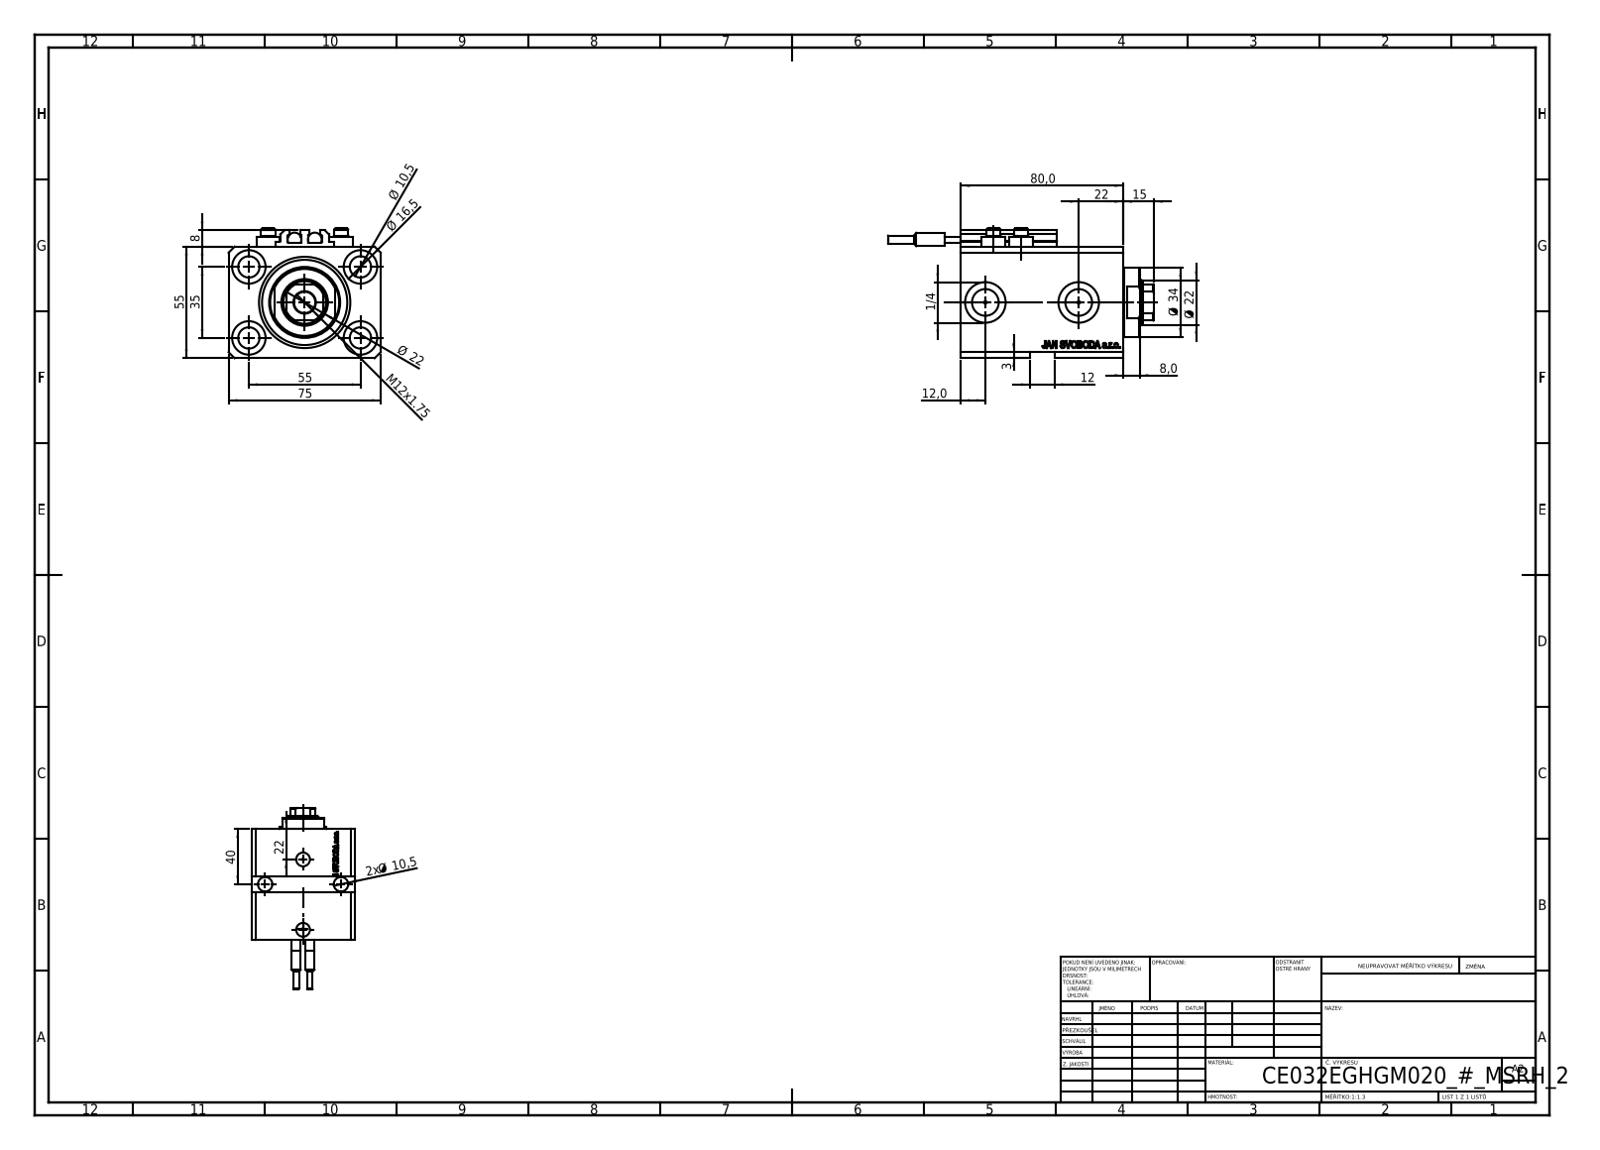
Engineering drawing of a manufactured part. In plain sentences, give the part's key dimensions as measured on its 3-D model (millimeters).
The part is named "V250CE_C_VCP; SWITCH_V250CE; V250CE_E_Body; V250CE_VC_E (+1 more)". Its 3-D file was written by "SolidWorks 2019 (CONFIG_CONTROL_DESIGN)". It is 10 solids with 1116 faces: 546 planar, 138 cylindrical and 432 other. Overall it measures 131 by 75 by 64 millimeters. Its volume is 287 467 cubic millimeters and its surface area 77 213 square millimeters. Round holes: 7 of diameter 10.5, 4 of diameter 1.25, 4 of diameter 4, 4 of diameter 16.5, 2 of diameter 10, 2 of diameter 13.16, 2 of diameter 20, 1 of diameter 22, 1 of diameter 32, 1 of diameter 45. Round bosses or shafts: 4 of diameter 11.6, 4 of diameter 7, 2 of diameter 6.8, 2 of diameter 6.5, 2 of diameter 4, 1 of diameter 34. Partial cylindrical surfaces (rounded edges, fillets, slot ends): 10 of radius 0.2, 1 of radius 10.5. The main face-to-face distances are 55, 75, 15, 3, 80, 65, 55.1, 9.9, 57, 70.1. The hole center spacings are 32.6, 55, 13.6, 14.09, 19.89, 20.12, 25.81, 28.48.
